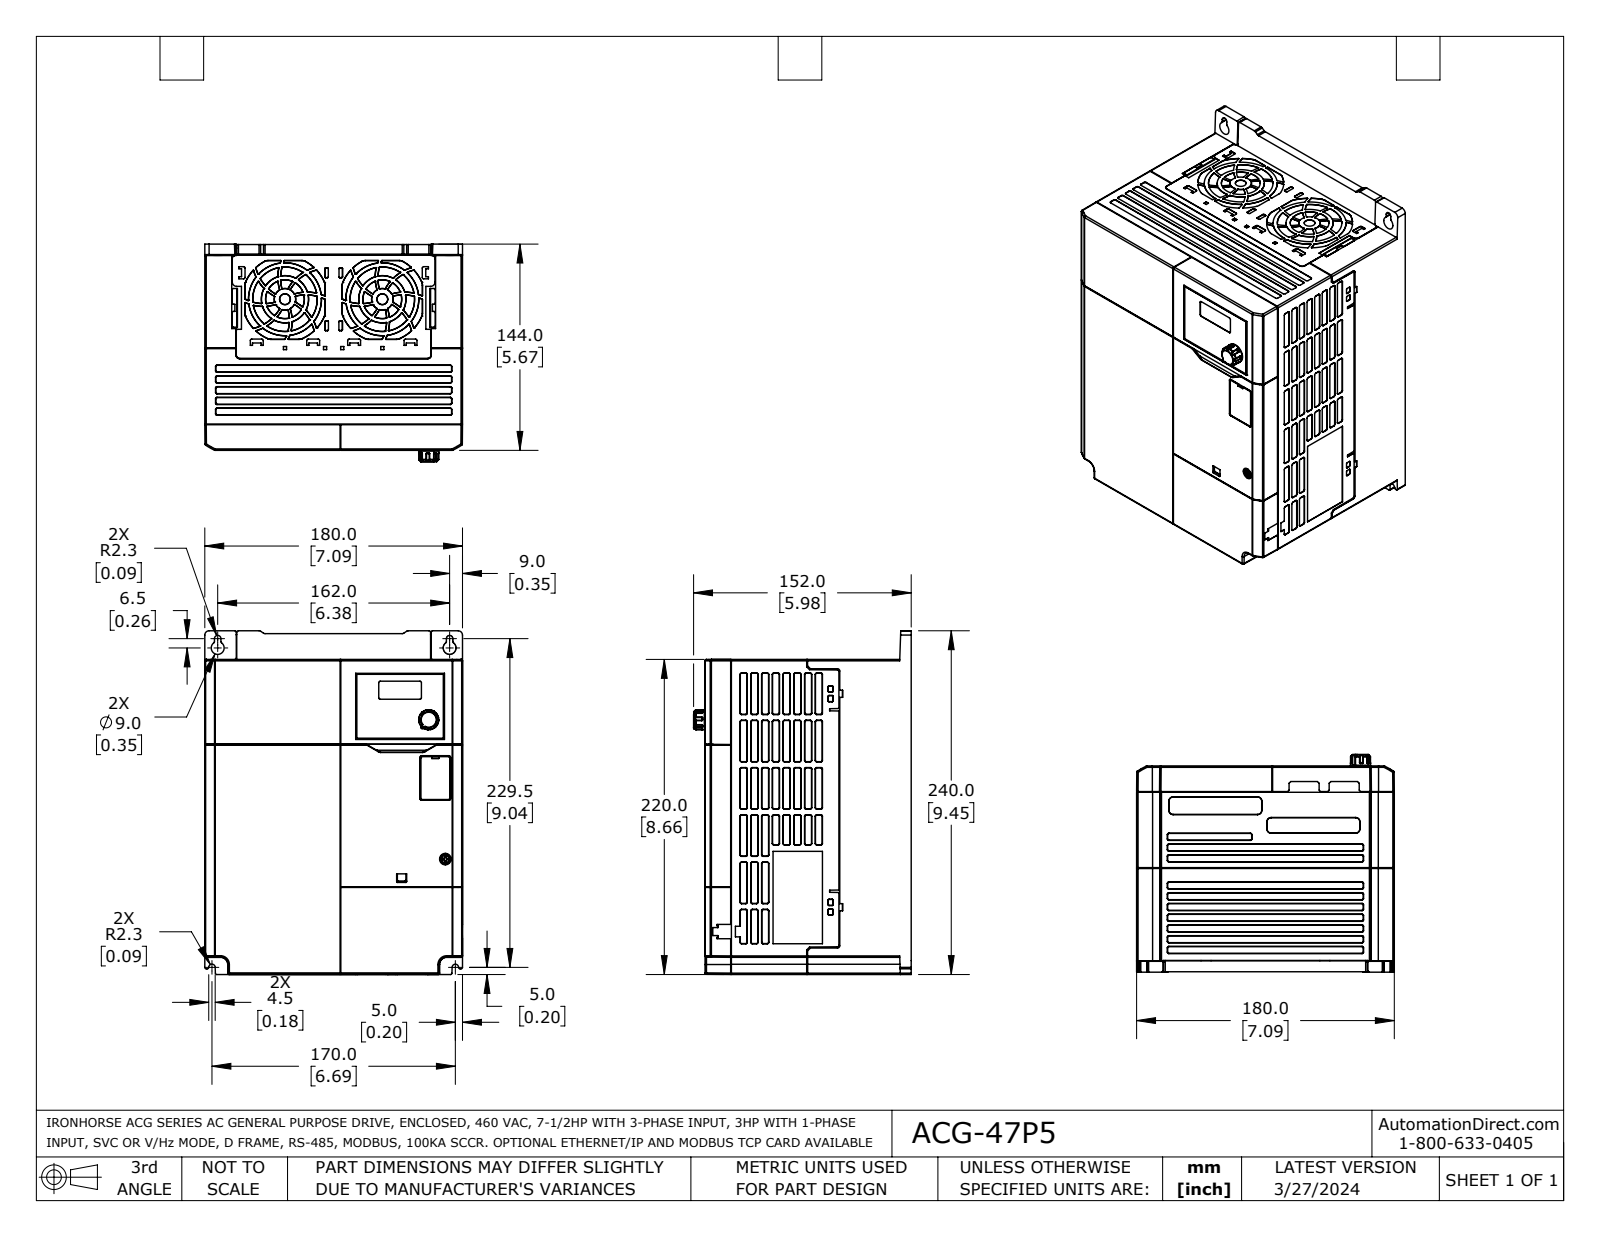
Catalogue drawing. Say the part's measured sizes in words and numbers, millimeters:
The part is named "ACG-47P5". Its 3-D file was written by "SolidWorks 2021 (AUTOMOTIVE_DESIGN)". It is 3 solids with 5218 faces: 2417 planar, 929 cylindrical and 1872 other. Overall it measures 240 by 180 by 152 millimeters. Its volume is 1 437 000 cubic millimeters and its surface area 486 000 square millimeters. Round holes: 1 of diameter 1, 1 of diameter 7, 1 of diameter 10.6, 1 of diameter 12. Round bosses or shafts: 1 of diameter 14, 1 of diameter 13.8, 1 of diameter 6. Partial cylindrical surfaces (rounded edges, fillets, slot ends): 587 of radius 0.5, 88 of radius 1, 65 of radius 0.2, 27 of radius 0.3, 16 of radius 0.6, 10 of radius 1.2, 5 of radius 2, 4 of radius 1.5. The main face-to-face distances are 135, 4.2, 139.2, 3.4, 135.8, 0.8, 1, 179, 3.2, 136. The hole center spacings are 7, 54.7, 55.7, 93.3, 98, 144.6.
